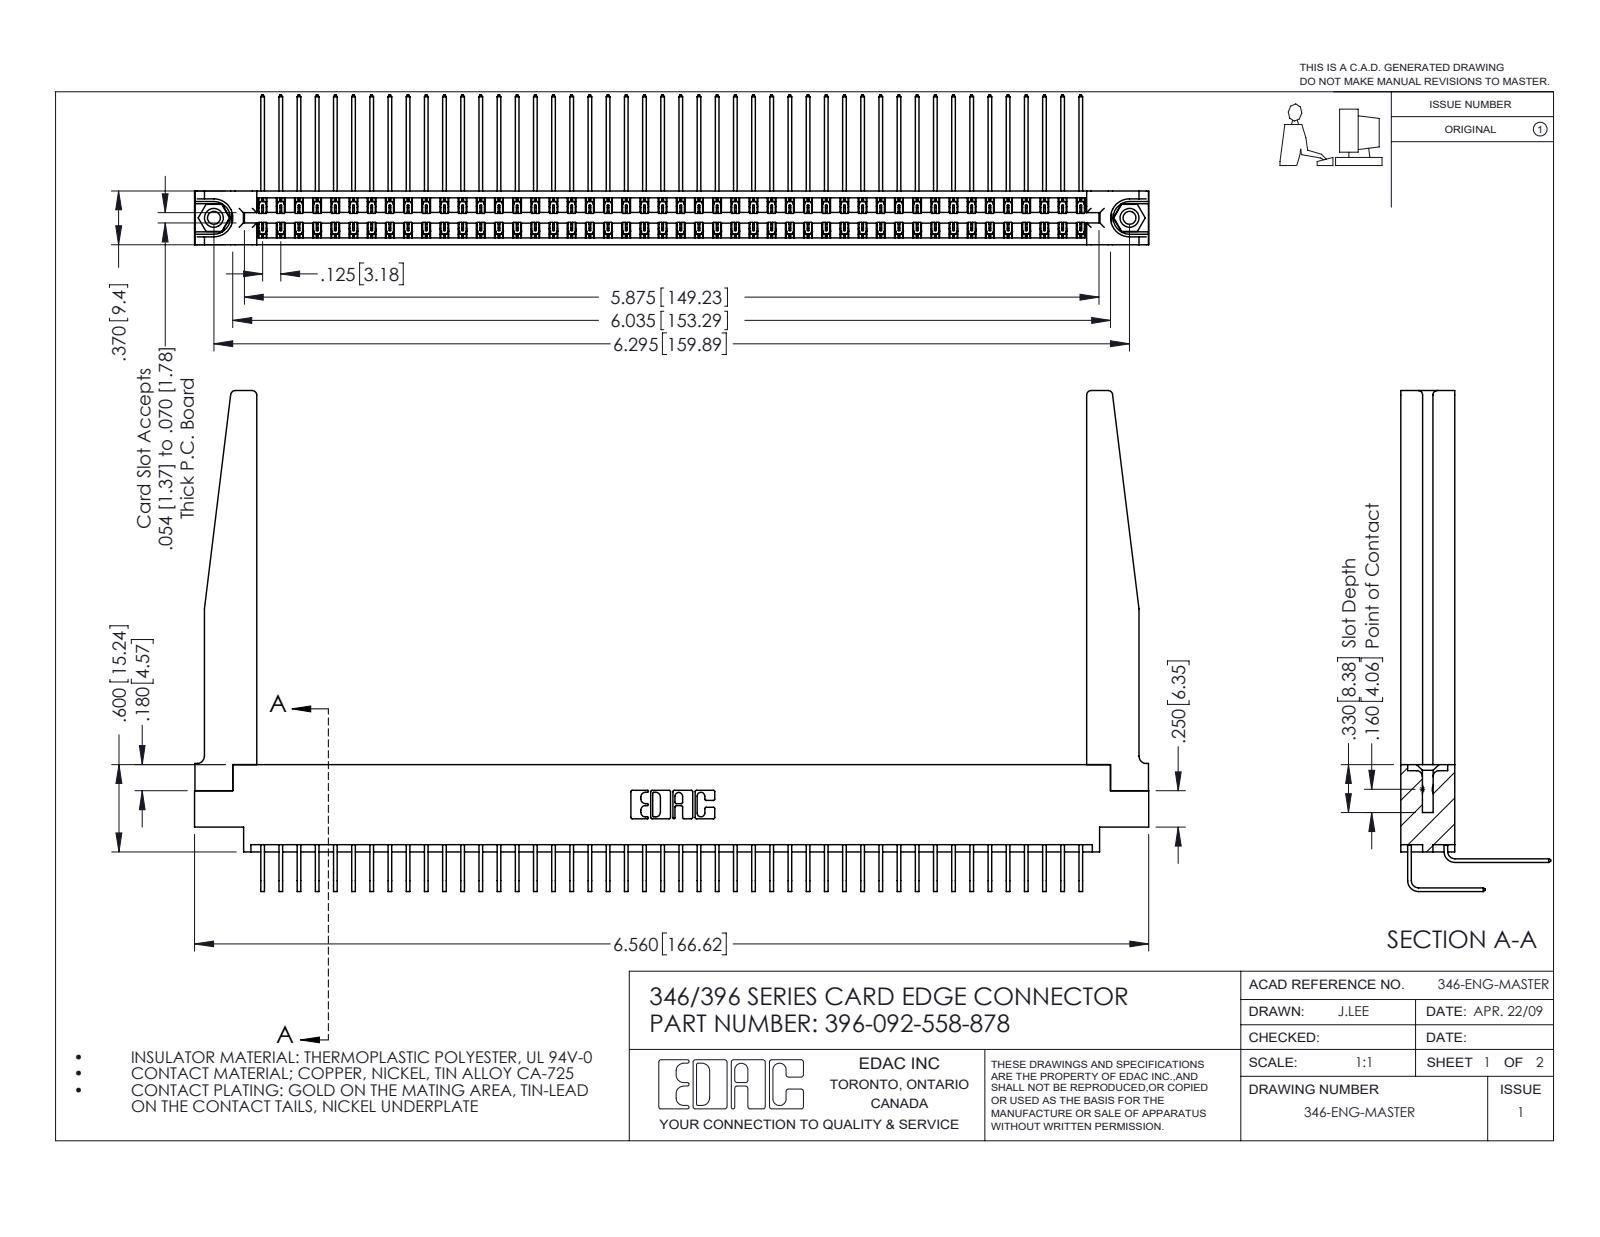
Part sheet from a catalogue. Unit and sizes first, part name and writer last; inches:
Units: inches
Overall size (bounding box): 6.56 × 3.443 × 1.03
Round holes (diameter × count): ⌀0.089 ×2, ⌀0.125 ×2, ⌀0.156 ×2, ⌀0.064 ×1
Round bosses / shafts (diameter × count): ⌀0.155 ×2
Partial cylindrical surfaces — rounded edges, fillets, slot ends (radius × count): R0.006 ×138, R0.01 ×22, R0.03 ×8, R0.007 ×6, R0.031 ×6, R0.05 ×4, R0.026 ×3, R0.014 ×2
Main face-to-face distances: 0.322, 0.37, 0.048, 0.072, 0.025, 0.298, 0.25, 0.148, 0.15, 0.275
Hole centre spacings: 0.246, 6.086, 6.295
Volume: 1.438 in³ · Surface area: 49.94 in²
Bodies: 97 solids, 5328 faces (3626 planar, 1650 cylindrical, 52 other)
Part name (STEP PRODUCT): 396-092-558-878; 345-250-001_345-250-001-102; 346-220-078_345-220-078; 345-292-001_558 Tail - 2 (+2 more)
STEP written by: SolidWorks 2016 (CONFIG_CONTROL_DESIGN)
